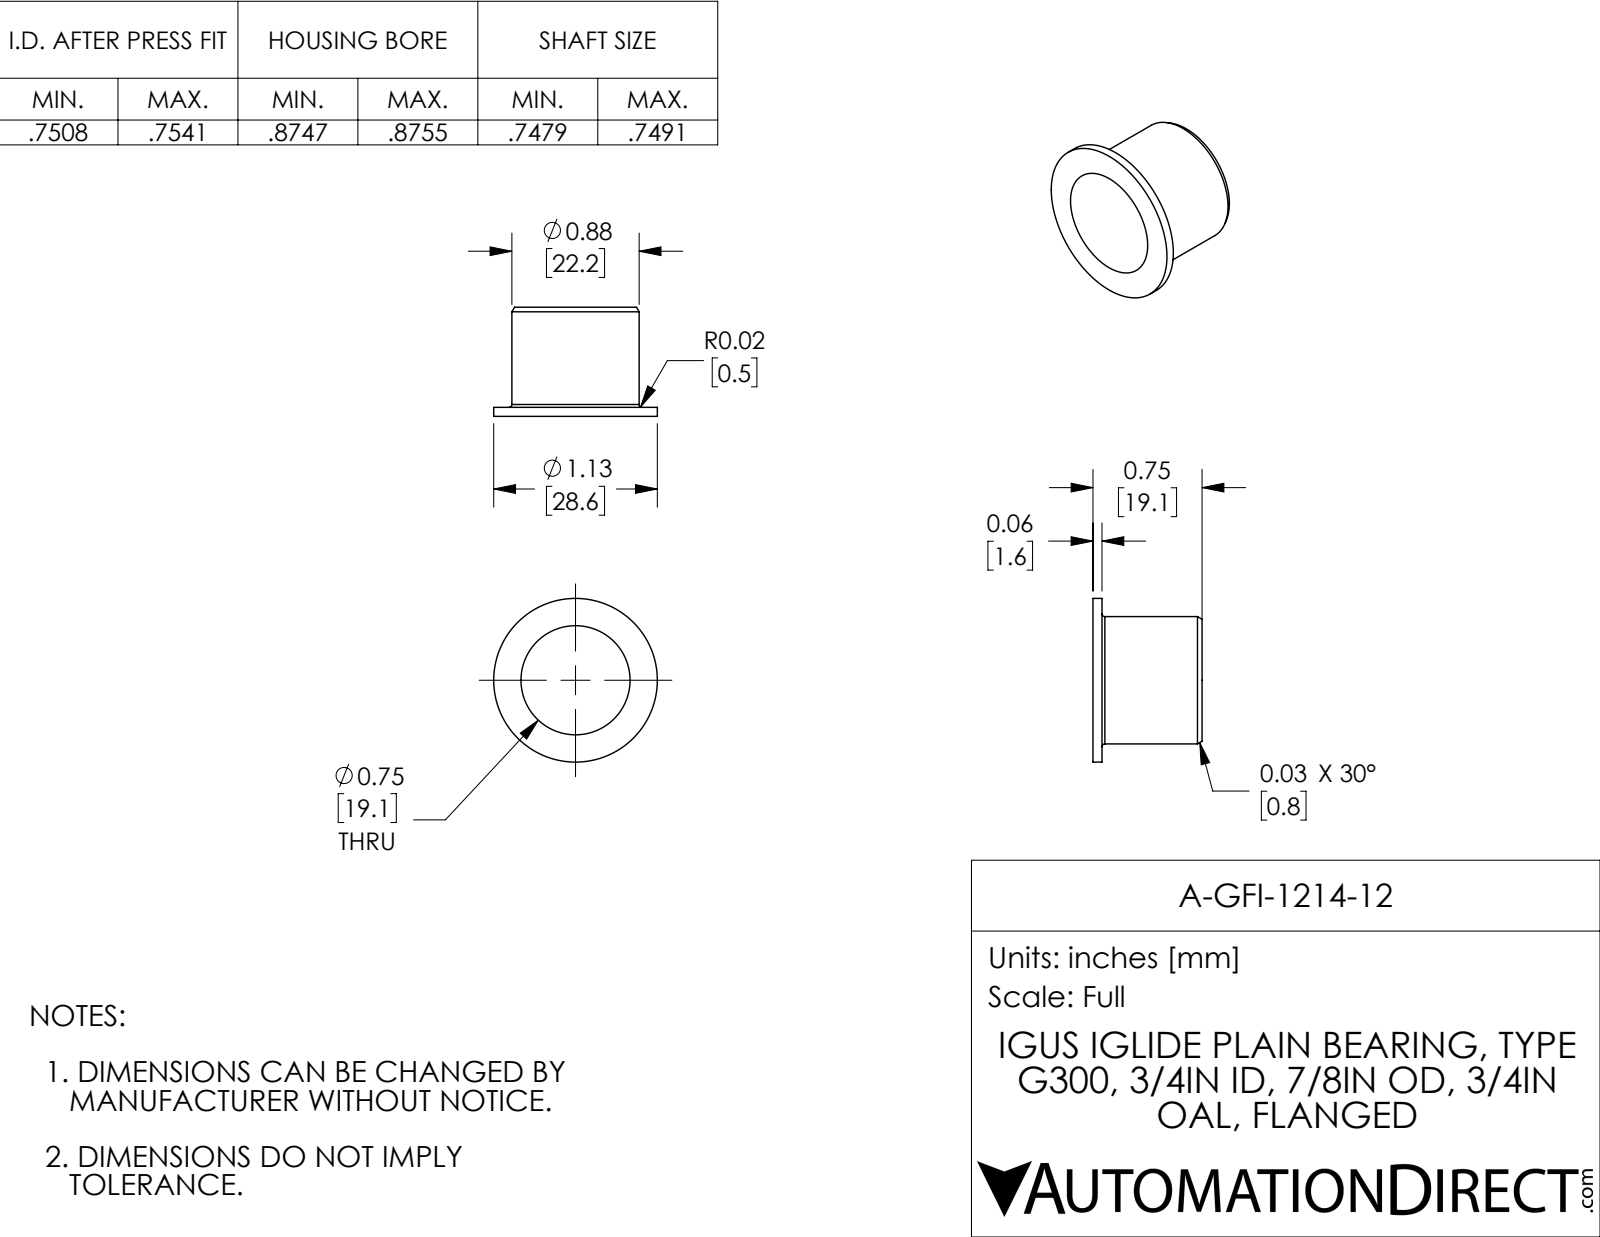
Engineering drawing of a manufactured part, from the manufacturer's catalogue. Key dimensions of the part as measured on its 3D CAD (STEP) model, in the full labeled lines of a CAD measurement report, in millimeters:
Part name (STEP PRODUCT): A-GFI-1214-12
STEP written by: SolidWorks 2017 (AUTOMOTIVE_DESIGN)
Units: millimetres
Bodies: 1 solid, 13 faces (3 planar, 6 cylindrical, 4 other)
Overall size (bounding box): 28.6 × 28.6 × 19.1
Volume: 2 340 mm³ · Surface area: 3 175 mm²
Round holes (diameter × count): ⌀19.1 ×1
Round bosses / shafts (diameter × count): ⌀28.6 ×1, ⌀22.2 ×1
Main face-to-face distances: 1.6, 19.1, 17.5
